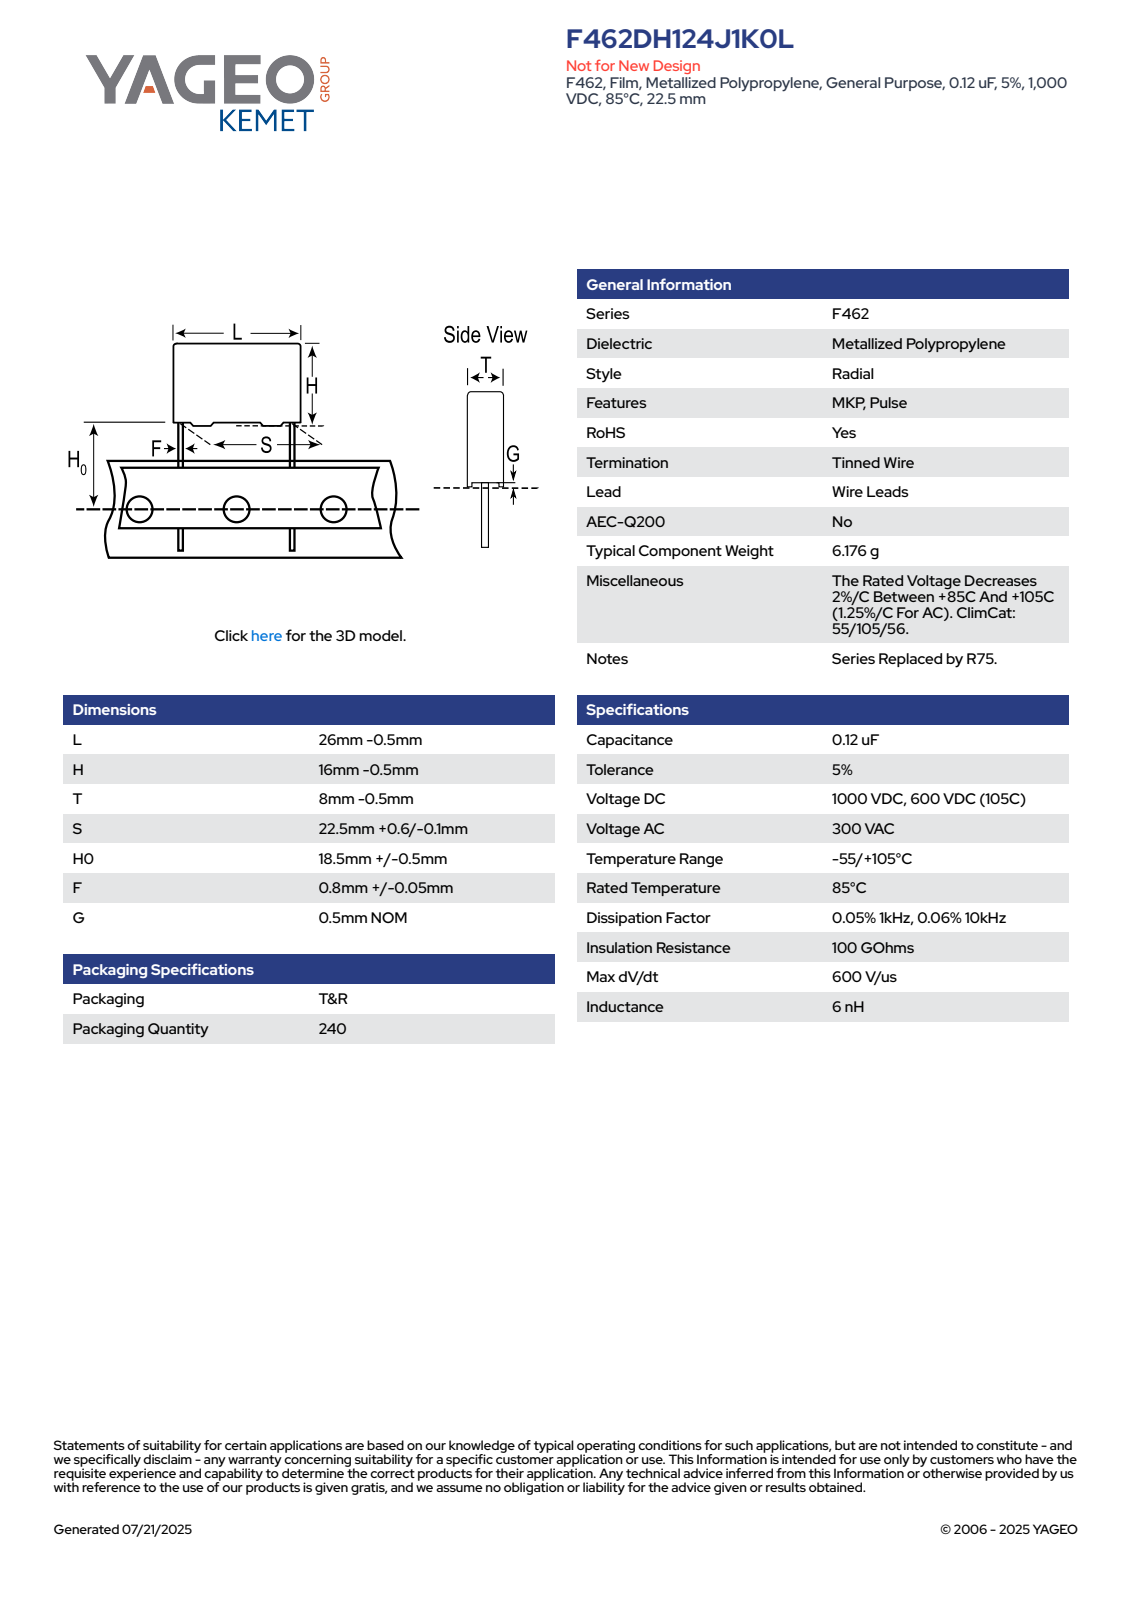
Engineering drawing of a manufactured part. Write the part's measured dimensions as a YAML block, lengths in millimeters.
part_name: "CFR_RBG_26X16X8_L25.5H15.5T7.5S22.5H019F0.85G0.5"
step_written_by: "SolidWorks 2014 (AUTOMOTIVE_DESIGN)"
units: millimeters
bodies: {solids: 4, faces: 89, planar: 81, cylindrical: 8, other: 0}
overall_size: [34.5, 25.5, 7.5]
volume: 2891
surface_area: 1550
round_bosses_or_shafts:
  - {diameter: 0.85, count: 2}
partial_cylinders:
  - {radius: 0.5, count: 4}
face_to_face_distances: [7.5, 15, 25.5, 0.43, 7.07, 0.5, 15.5, 6.64, 19, 19.5]
